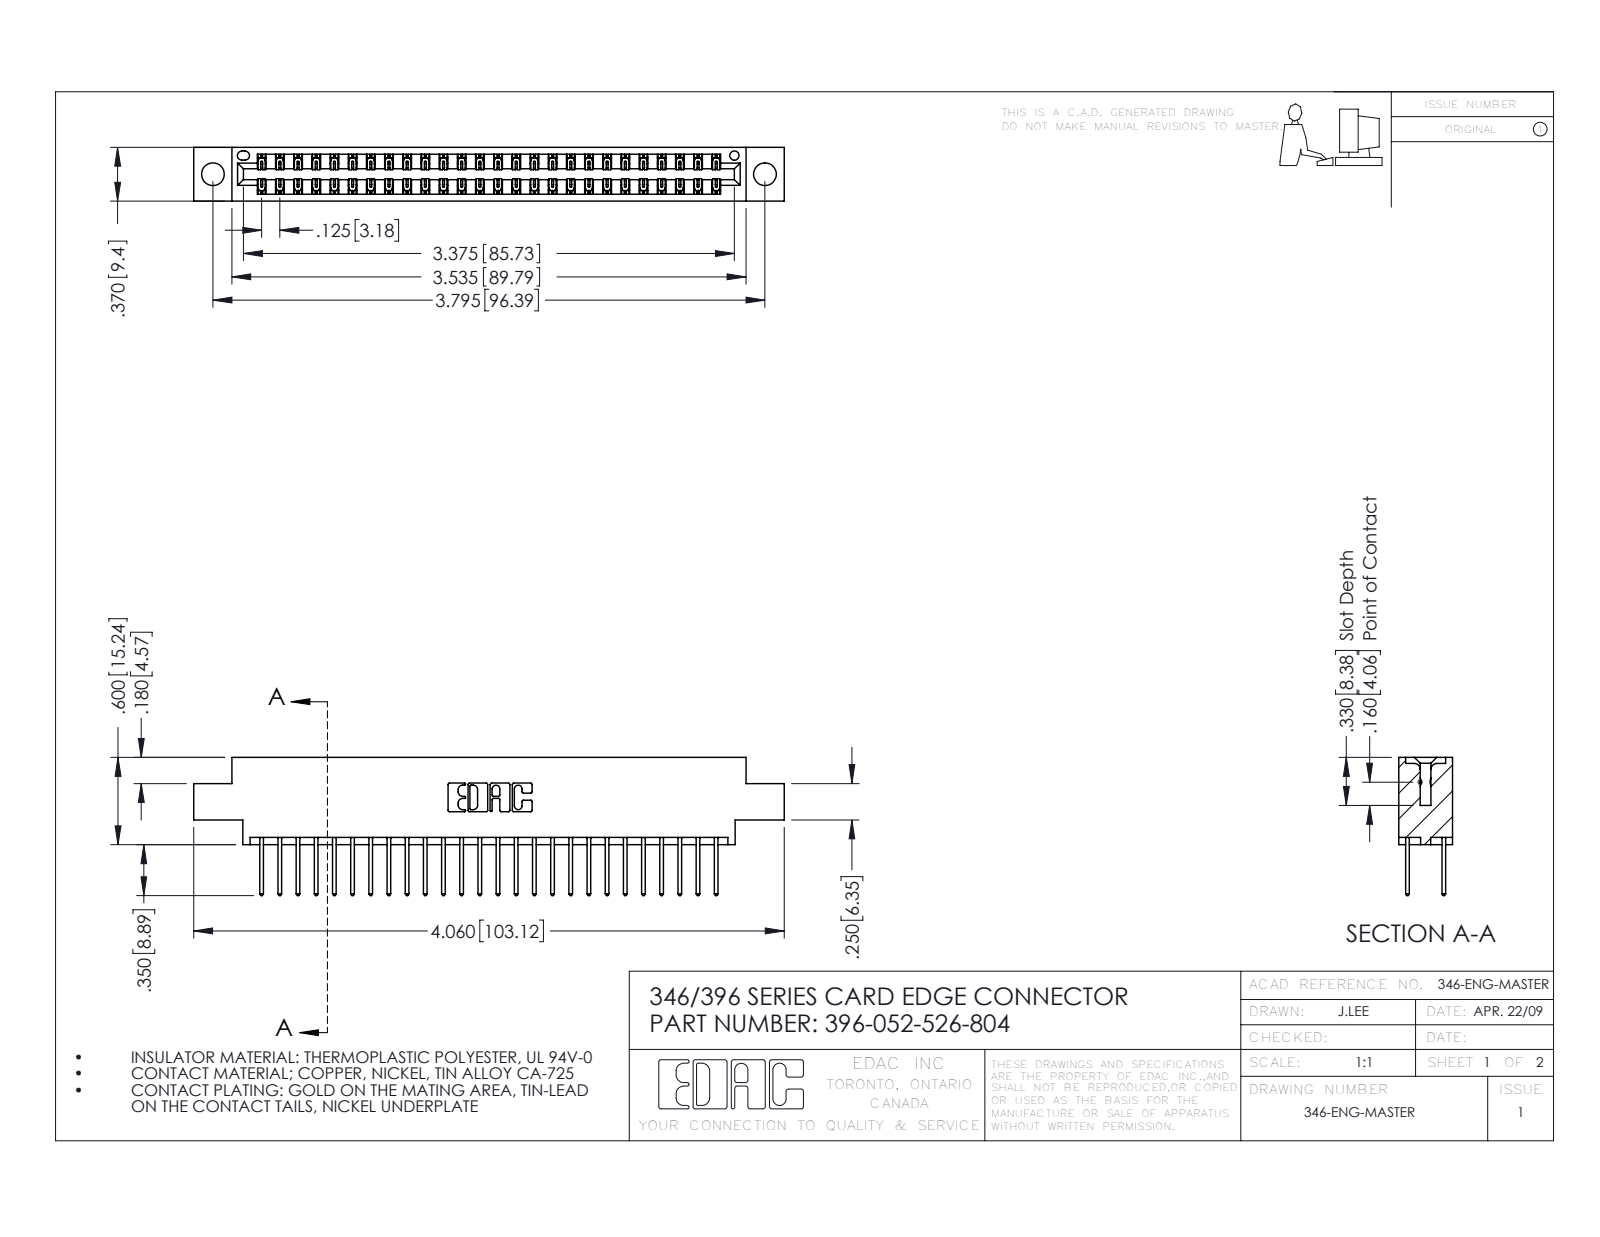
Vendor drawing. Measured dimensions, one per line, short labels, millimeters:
name: 345-292-001_345-293-126; 396-052-526-804; 346 Part_0.170 Offset - 0.156 Dia-TH
written by: SolidWorks 2016 (CONFIG_CONTROL_DESIGN)
unit: mm
bodies: 53 solids, 2830 faces (1900 planar, 930 cylindrical, 0 other)
size: 103.1 × 24.1 × 9.4
volume: 9 770 mm³; area: 13 560 mm²
holes: 2× ⌀4, 1× ⌀1.6
rounds: 78× R0.2, 52× R0.3, 22× R0.3, 6× R0.2, 6× R0.8, 3× R0.7, 2× R0.4, 2× R0.6
face distances: 1.2, 8.2, 6.4, 9.4, 1.8, 7.6, 0.6, 7, 3.8, 5.6
hole spacings: 6.2, 91.1, 96.4
